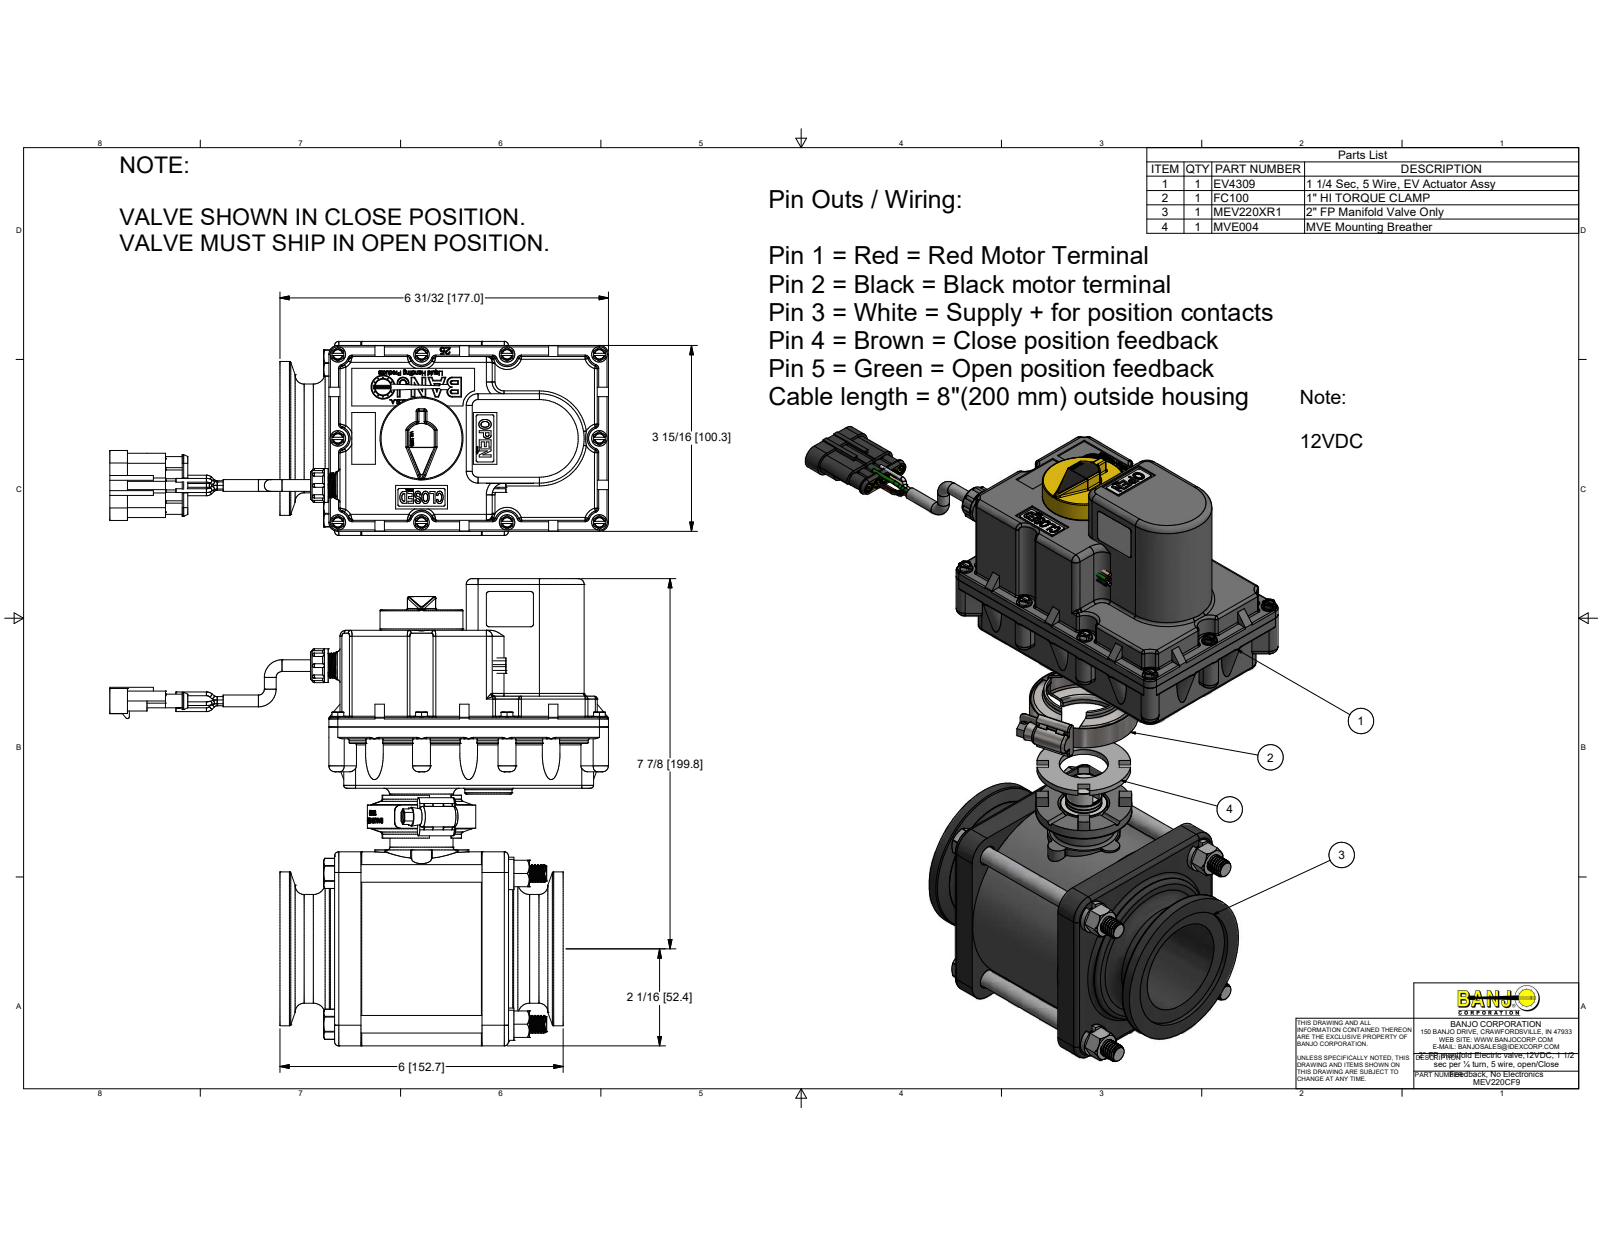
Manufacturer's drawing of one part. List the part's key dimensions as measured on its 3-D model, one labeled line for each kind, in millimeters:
Part name (STEP PRODUCT): MEV25254AX; MEV25254A; VE25255SSH; MEV25151SS (+8 more)
STEP written by: Autodesk Inventor 2014 (AUTOMOTIVE_DESIGN)
Units: millimetres
Bodies: 74 solids, 6534 faces (2627 planar, 1740 cylindrical, 2167 other)
Overall size (bounding box): 300.92 × 252.22 × 104.78
Volume: 1 328 000 mm³ · Surface area: 505 849 mm²
Round holes (diameter × count): ⌀2.79 ×10, ⌀4.06 ×10, ⌀5.08 ×10, ⌀3.05 ×6, ⌀3.81 ×6, ⌀1.4 ×5, ⌀5.5 ×5, ⌀4.47 ×4, ⌀7.81 ×4, ⌀9.78 ×4, ⌀11.13 ×4, ⌀9.52 ×3
Round bosses / shafts (diameter × count): ⌀8.24 ×60, ⌀2.03 ×19, ⌀8.33 ×10, ⌀3.51 ×10, ⌀2.62 ×8, ⌀8 ×6, ⌀7.62 ×6, ⌀17.46 ×5
Partial cylindrical surfaces — rounded edges, fillets, slot ends (radius × count): R0.76 ×125, R0.51 ×63, R1.52 ×47, R3.17 ×28, R8 ×24, R12.7 ×24, R1.59 ×22, R0.5 ×21
Main face-to-face distances: 5.08, 3.18, 27.94, 1.9, 6.98, 21.59, 3.17, 33.02, 82.04, 20.07
Hole centre spacings: 42.68, 52.25, 52.27, 60.34, 60.36, 33.76, 45.34, 6
